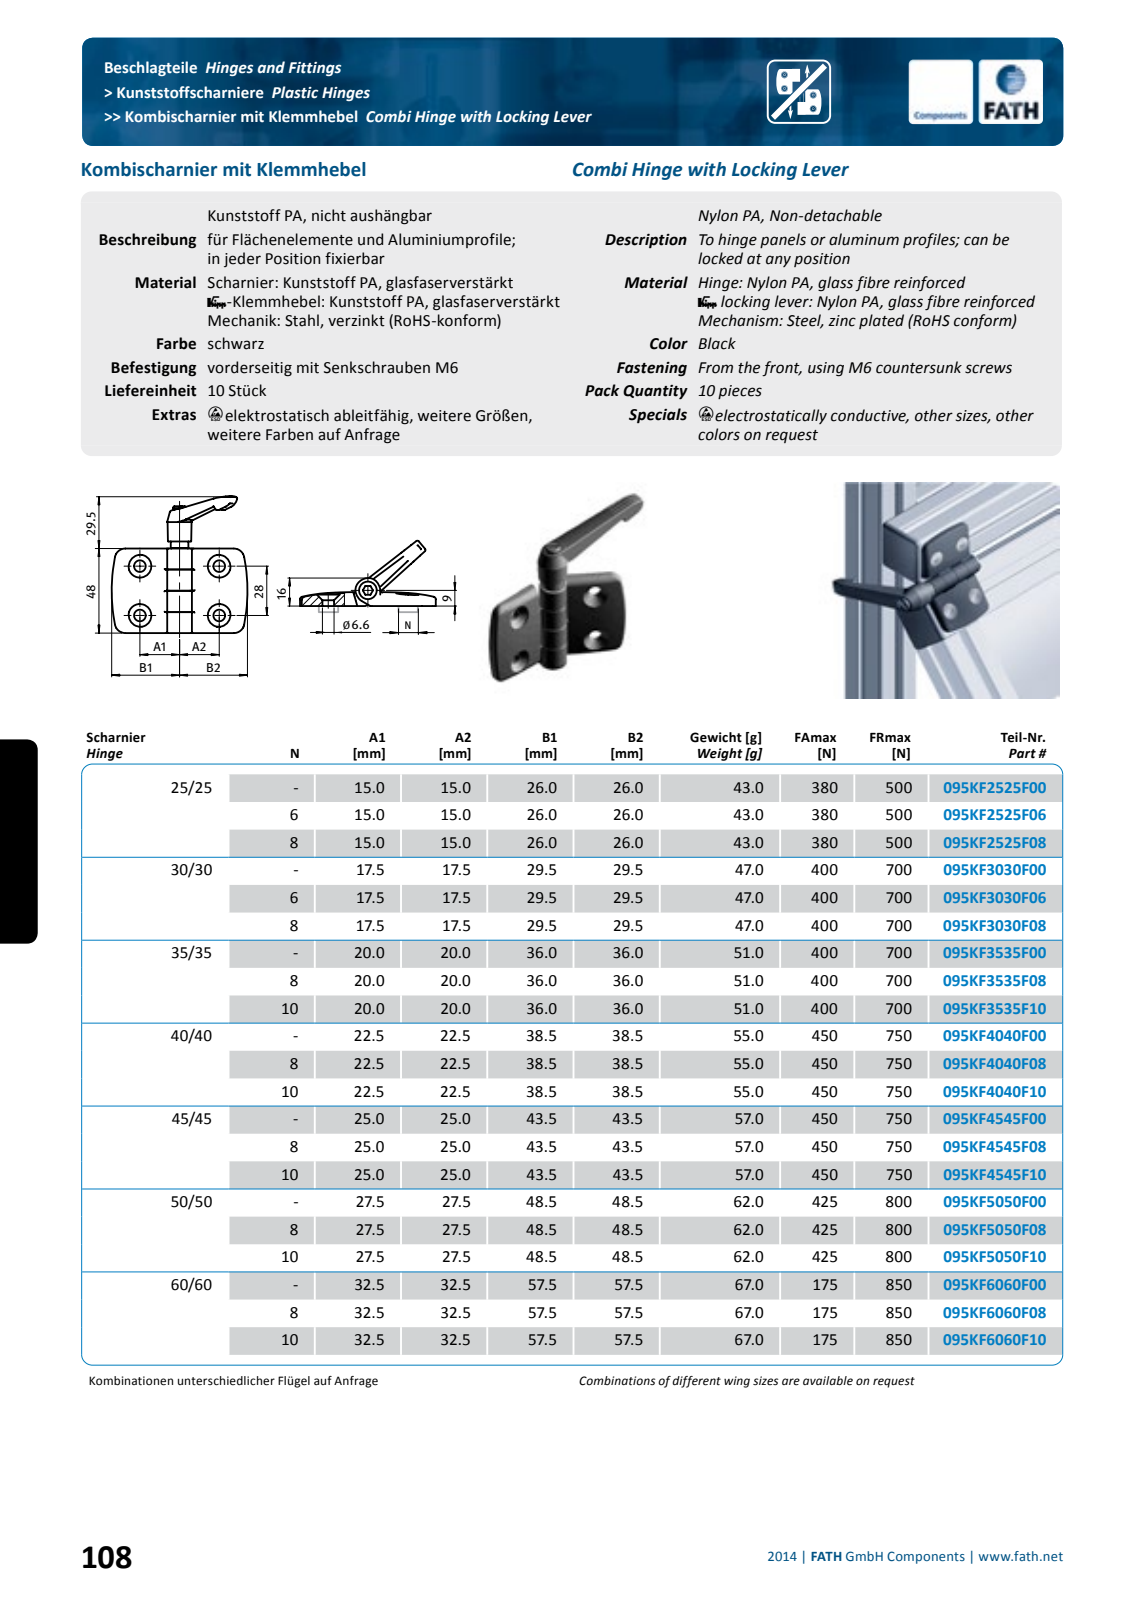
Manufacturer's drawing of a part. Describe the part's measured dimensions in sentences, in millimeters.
The part is named "fath_095kf4040f08_1; fath_095kf4040f08_2; fath_095kf4040f08_3; fath_095kf4040f08_4 (+1 more)". Its 3-D file was written by "Spatial InterOp 3D (automotive_design)". It is 5 solids with 685 faces: 156 planar, 115 cylindrical and 414 other. Overall it measures 78 by 77 by 39.6 millimeters. Its volume is 27 516 cubic millimeters and its surface area 16 896 square millimeters. Round holes: 4 of diameter 6.6, 1 of diameter 4.2, 1 of diameter 6, 1 of diameter 8.2, 1 of diameter 9.8. Round bosses or shafts: 1 of diameter 14, 1 of diameter 10, 1 of diameter 9, 1 of diameter 8, 1 of diameter 7, 1 of diameter 4.4. Partial cylindrical surfaces (rounded edges, fillets, slot ends): 20 of radius 0.3, 12 of radius 0.5, 6 of radius 0.4, 4 of radius 6, 4 of radius 6.5, 3 of radius 0.25, 2 of radius 4, 2 of radius 100. The main face-to-face distances are 1.5, 36.1, 11.9, 12, 23.9, 3, 24.1, 12.2, 24.2, 4.9. The hole center spacings are 28, 45, 53.
